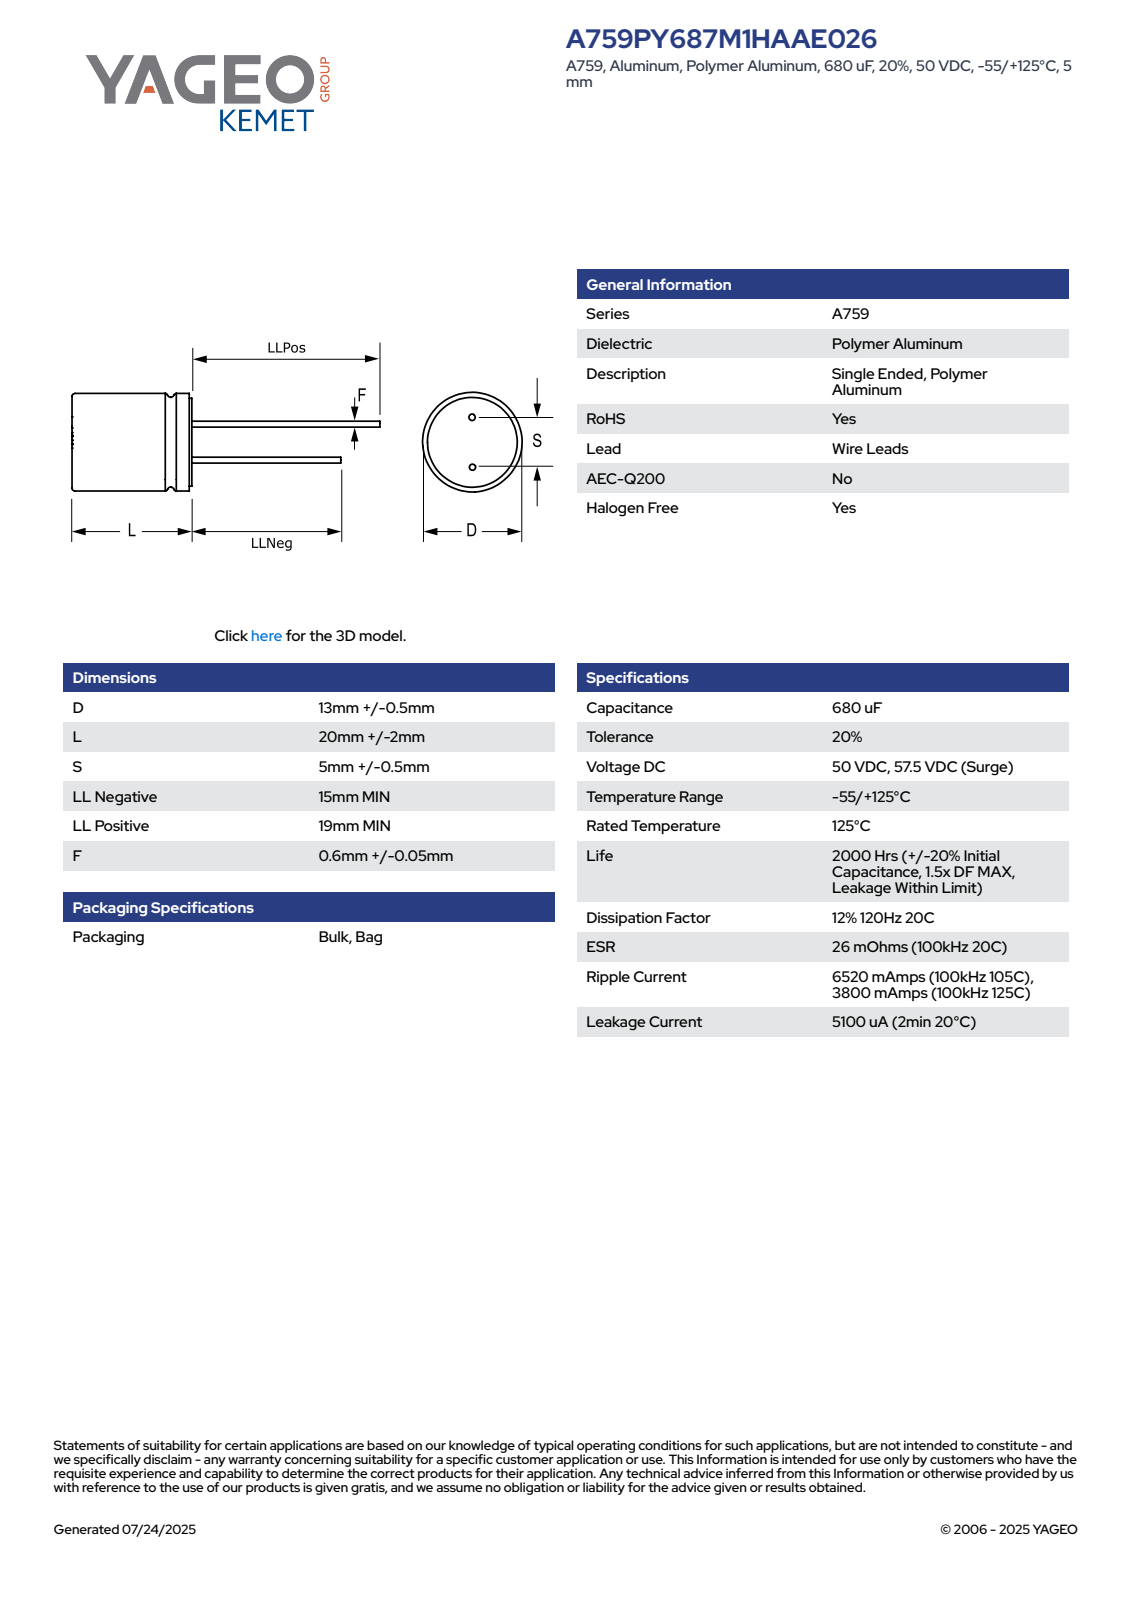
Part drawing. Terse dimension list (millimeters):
name: CAR_KP_13X20_D13.5L22S5F0.65
written by: SolidWorks 2014 (AUTOMOTIVE_DESIGN)
unit: mm
bodies: 4 solids, 75 faces (61 planar, 8 cylindrical, 6 other)
size: 41.01 × 13.5 × 13.5
volume: 3 130 mm³; area: 1 326 mm²
bosses: 2× ⌀0.65, 1× ⌀13.5
face distances: 22, 22.01, 37.01, 41.01, 37, 41, 15, 19, 4, 1.49
